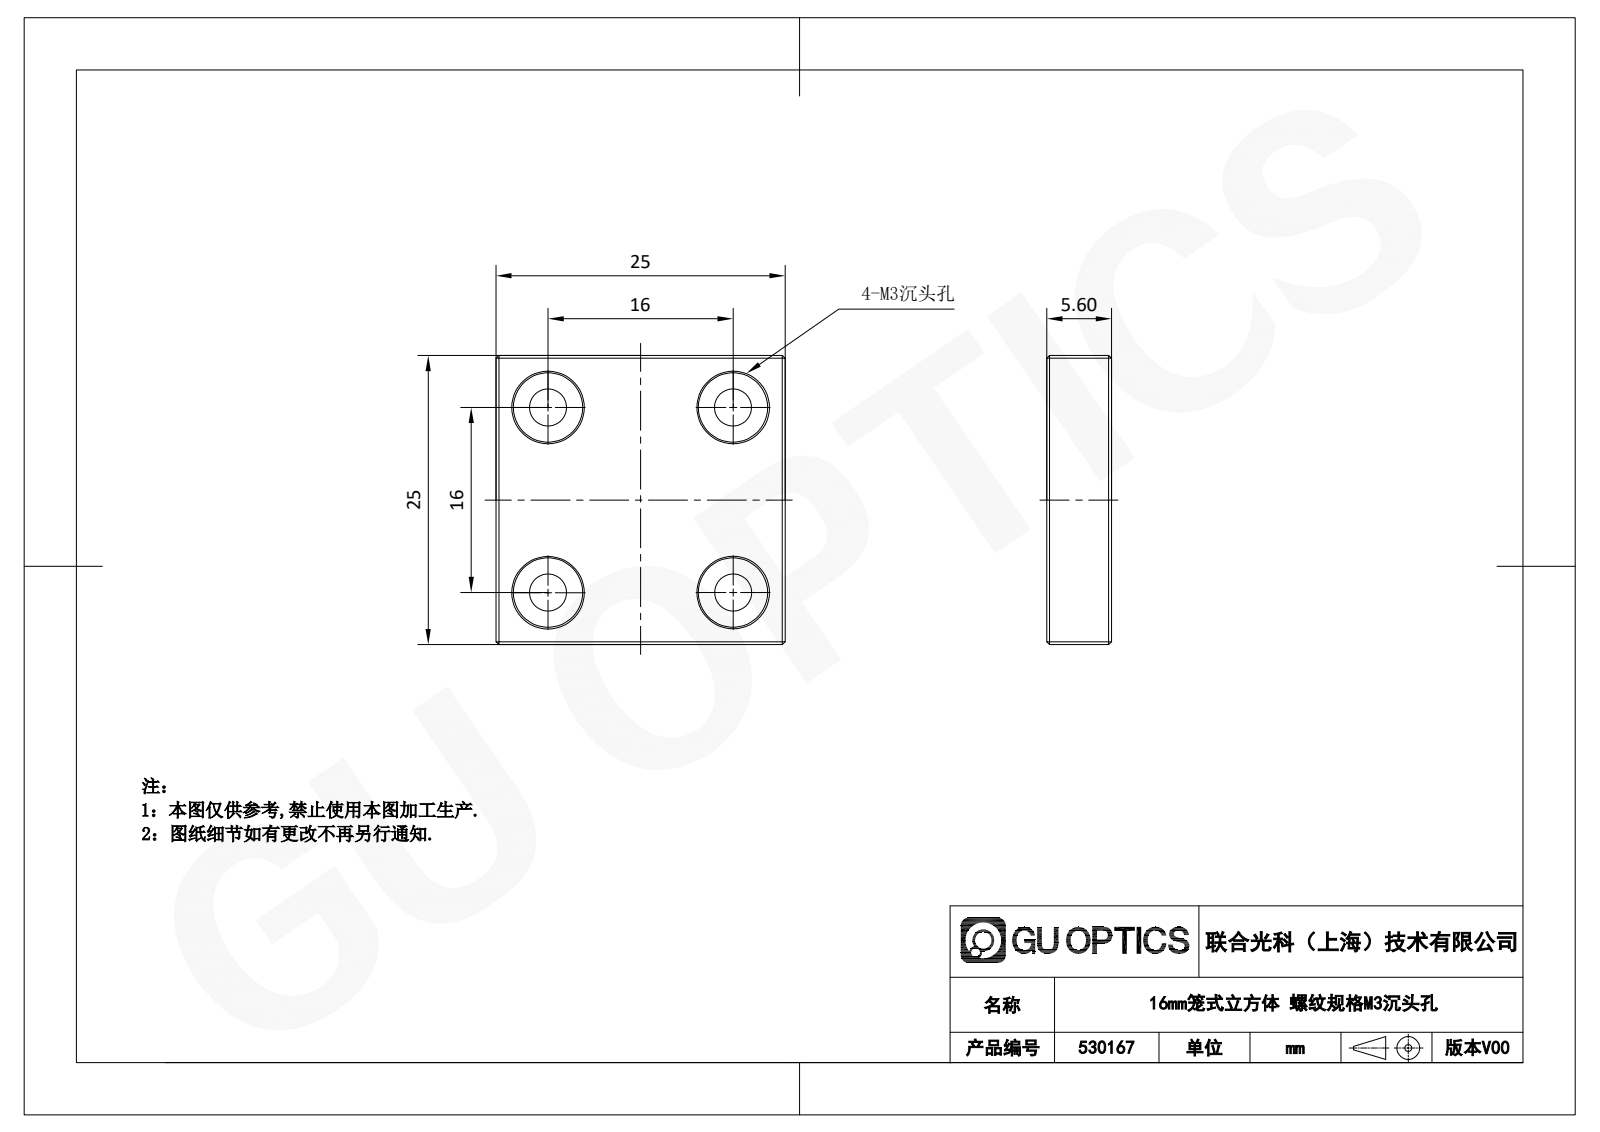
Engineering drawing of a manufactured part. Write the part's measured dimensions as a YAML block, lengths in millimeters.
part_name: "530167"
step_written_by: "SolidWorks 2020 (CONFIG_CONTROL_DESIGN)"
units: millimeters
bodies: {solids: 1, faces: 46, planar: 30, cylindrical: 8, other: 8}
overall_size: [25, 25, 5.6]
volume: 3069
surface_area: 2034
round_holes:
  - {diameter: 3.2, count: 4}
  - {diameter: 6, count: 4}
face_to_face_distances: [5.6, 25, 2.6, 3, 21.28, 35, 31.5]
hole_center_spacings: [16, 22.63]
